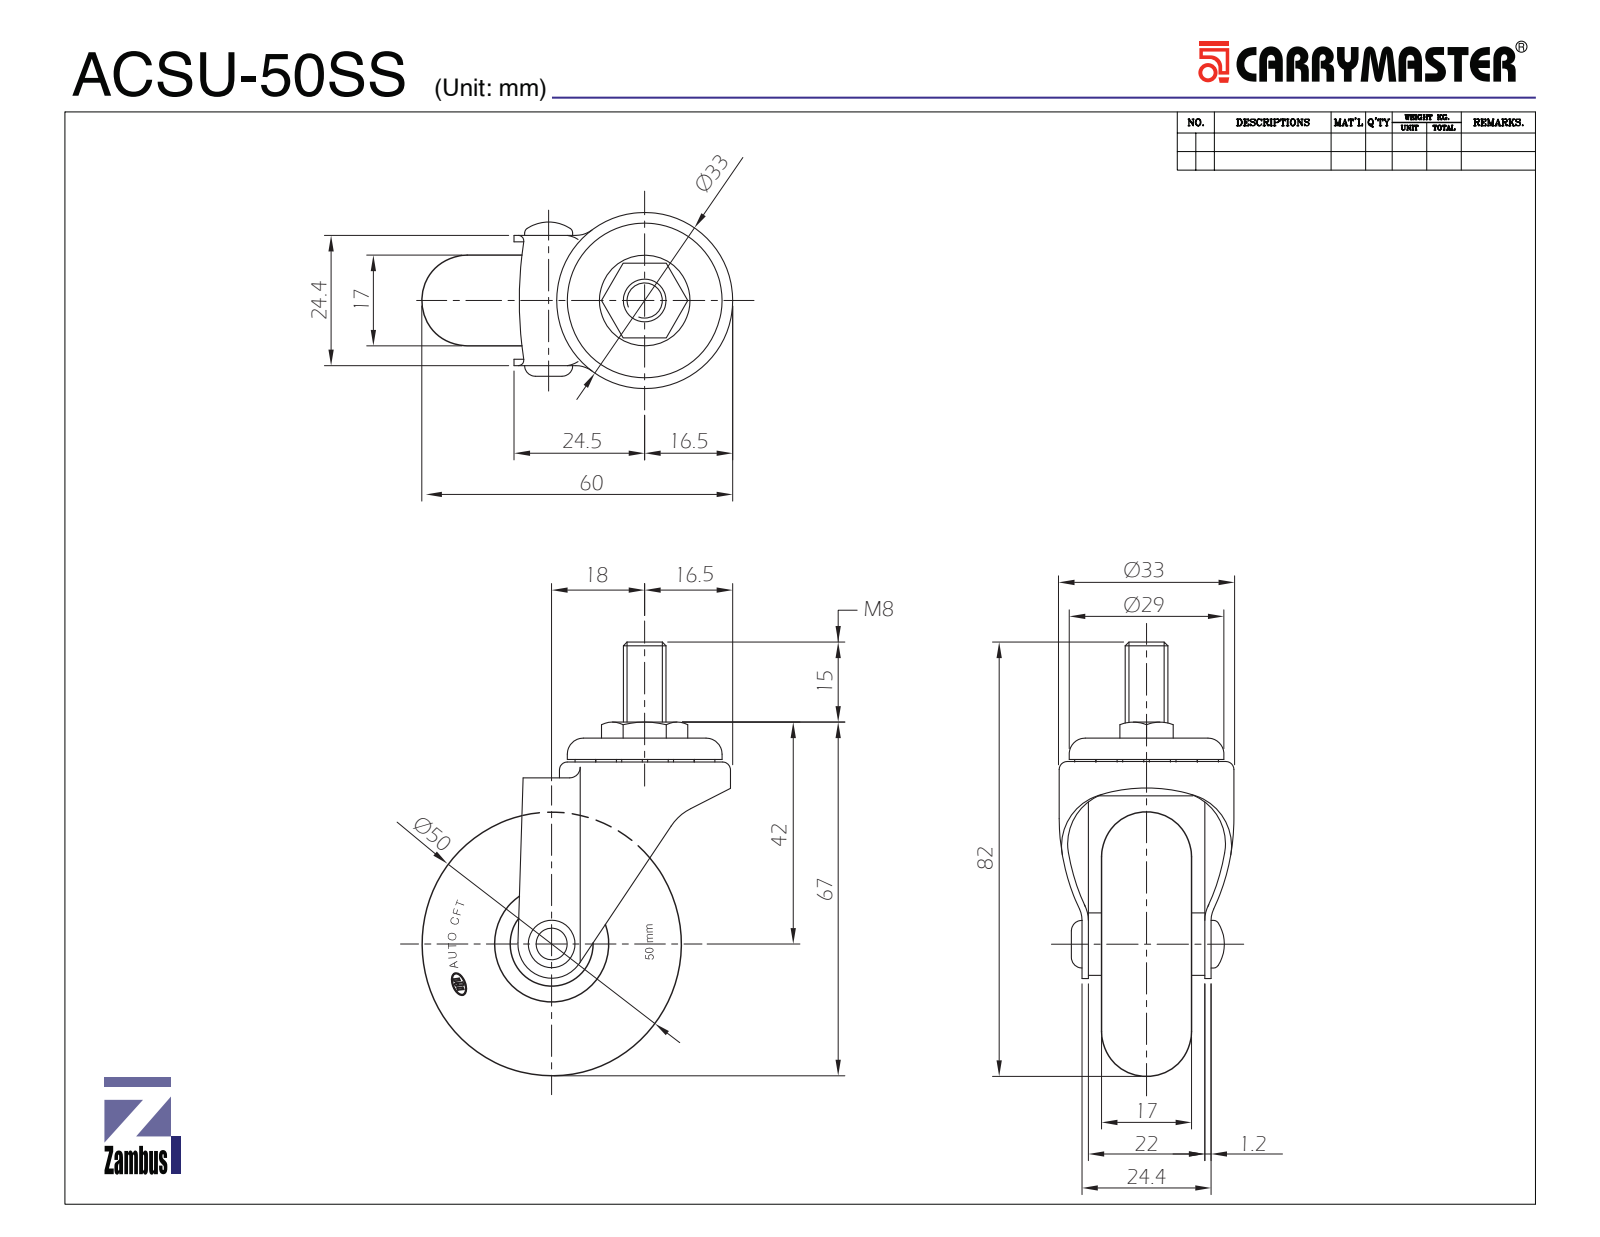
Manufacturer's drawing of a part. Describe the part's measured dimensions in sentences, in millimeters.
The part is named "ACSU-50SS". Its 3-D file was written by "SolidWorks 2015 (CONFIG_CONTROL_DESIGN)". It is 48 solids with 485 faces: 82 planar, 183 cylindrical and 220 other. Overall it measures 82.06 by 58.2 by 32.4 millimeters. Its volume is 38 428 cubic millimeters and its surface area 26 807 square millimeters. Round holes: 1 of diameter 6, 1 of diameter 7, 1 of diameter 8, 1 of diameter 10.35, 1 of diameter 13, 1 of diameter 13.75, 1 of diameter 16, 1 of diameter 22, 1 of diameter 26.5, 1 of diameter 30. Round bosses or shafts: 1 of diameter 29, 1 of diameter 28.9, 1 of diameter 16, 1 of diameter 11, 1 of diameter 10.5, 1 of diameter 10.25, 1 of diameter 10, 1 of diameter 9. Partial cylindrical surfaces (rounded edges, fillets, slot ends): 32 of radius 1, 2 of radius 2, 2 of radius 8.8, 2 of radius 10, 1 of radius 7, 1 of radius 13.5, 1 of radius 16.2. The main face-to-face distances are 1.2, 17, 19.5, 3.7, 20.7, 23.2, 2.5, 0.56, 24.4, 22.
